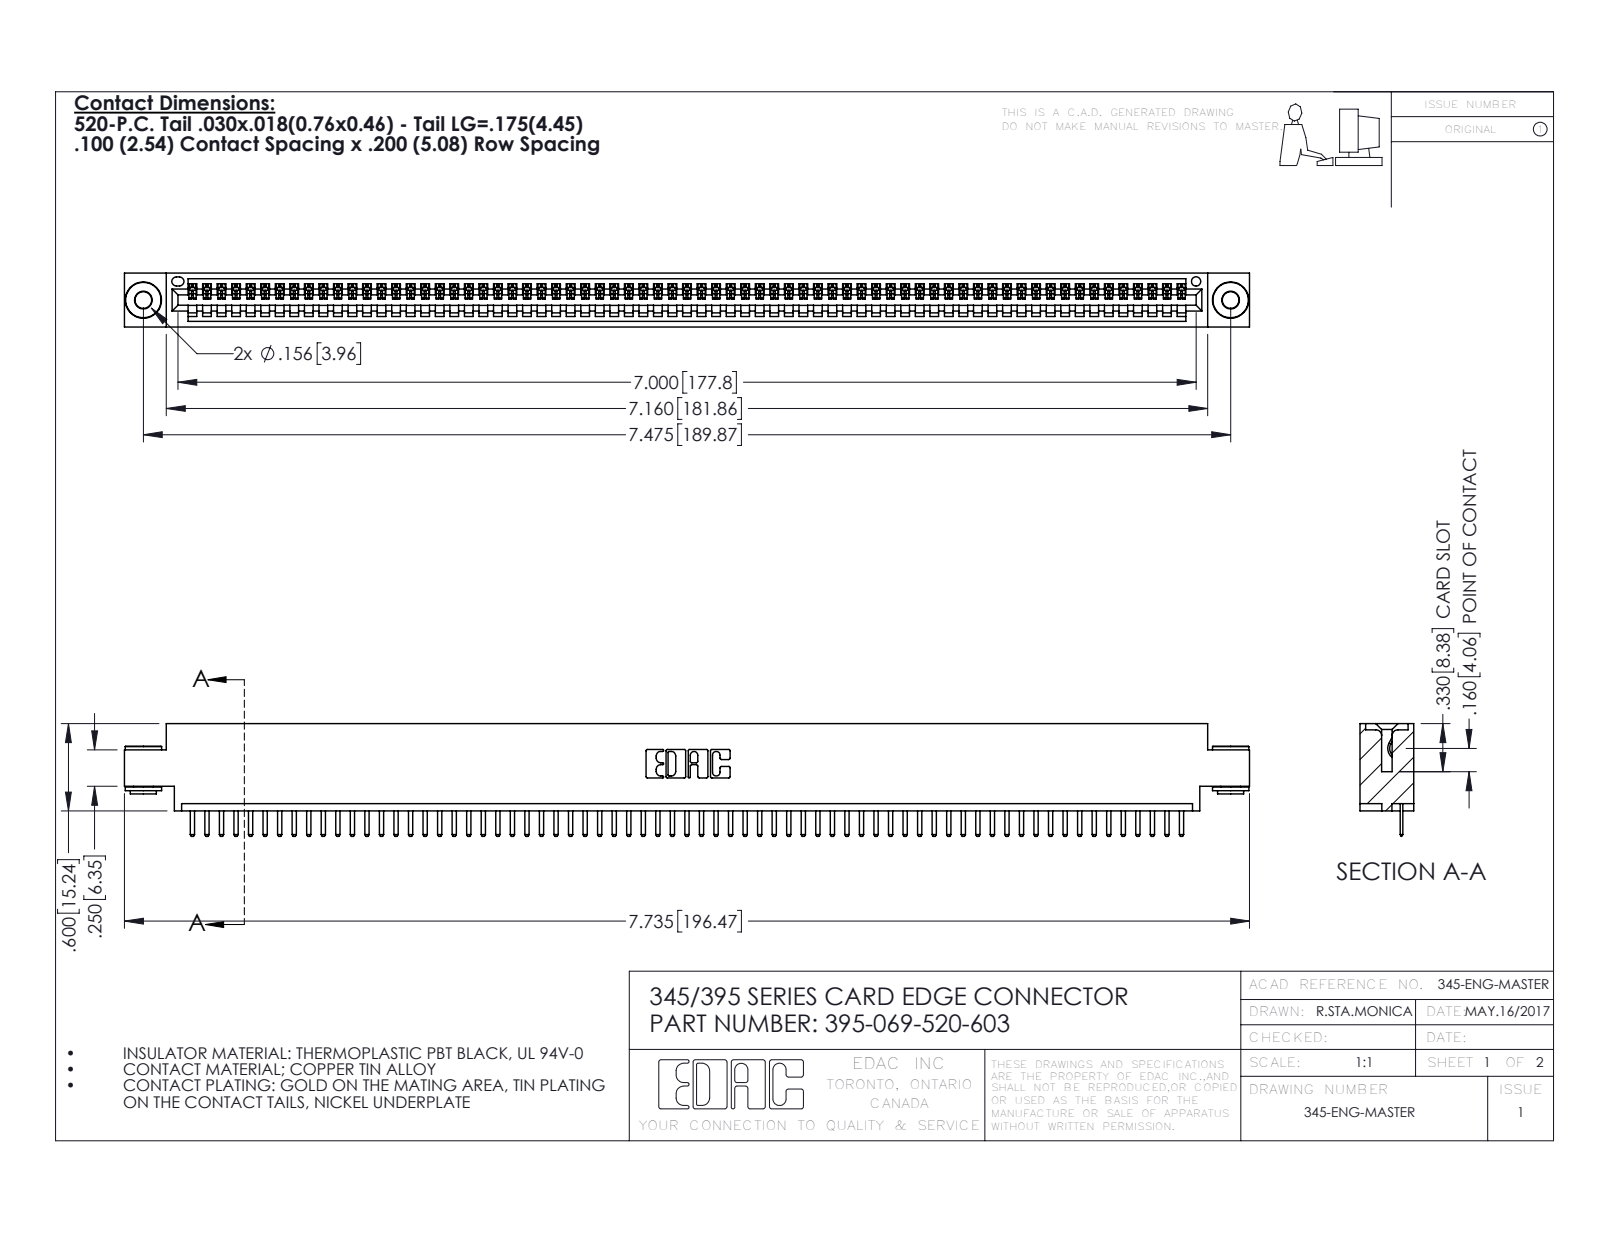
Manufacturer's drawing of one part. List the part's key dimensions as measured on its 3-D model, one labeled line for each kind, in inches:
Part name (STEP PRODUCT): 395-069-520-603; 345-250-002_345-250-002-102; 345-292-001_345-293-120; 345 Part_0.170 Offset - 0.156 Dia-TH
STEP written by: SolidWorks 2016 (CONFIG_CONTROL_DESIGN)
Units: inches
Bodies: 72 solids, 4446 faces (2992 planar, 1446 cylindrical, 8 other)
Overall size (bounding box): 7.735 × 0.775 × 0.37
Volume: 1.134 in³ · Surface area: 38.38 in²
Round holes (diameter × count): ⌀0.116 ×2, ⌀0.156 ×2, ⌀0.064 ×1
Round bosses / shafts (diameter × count): ⌀0.25 ×2, ⌀0.18 ×2, ⌀0.136 ×2
Partial cylindrical surfaces — rounded edges, fillets, slot ends (radius × count): R0.01 ×140, R0.006 ×138, R0.01 ×22, R0.007 ×6, R0.031 ×6, R0.026 ×3, R0.031 ×2, R0.04 ×2
Main face-to-face distances: 0.072, 0.298, 0.37, 0.2, 0.098, 0.272, 0.025, 0.225, 0.072, 0.175
Hole centre spacings: 0.27, 7.239, 7.475
